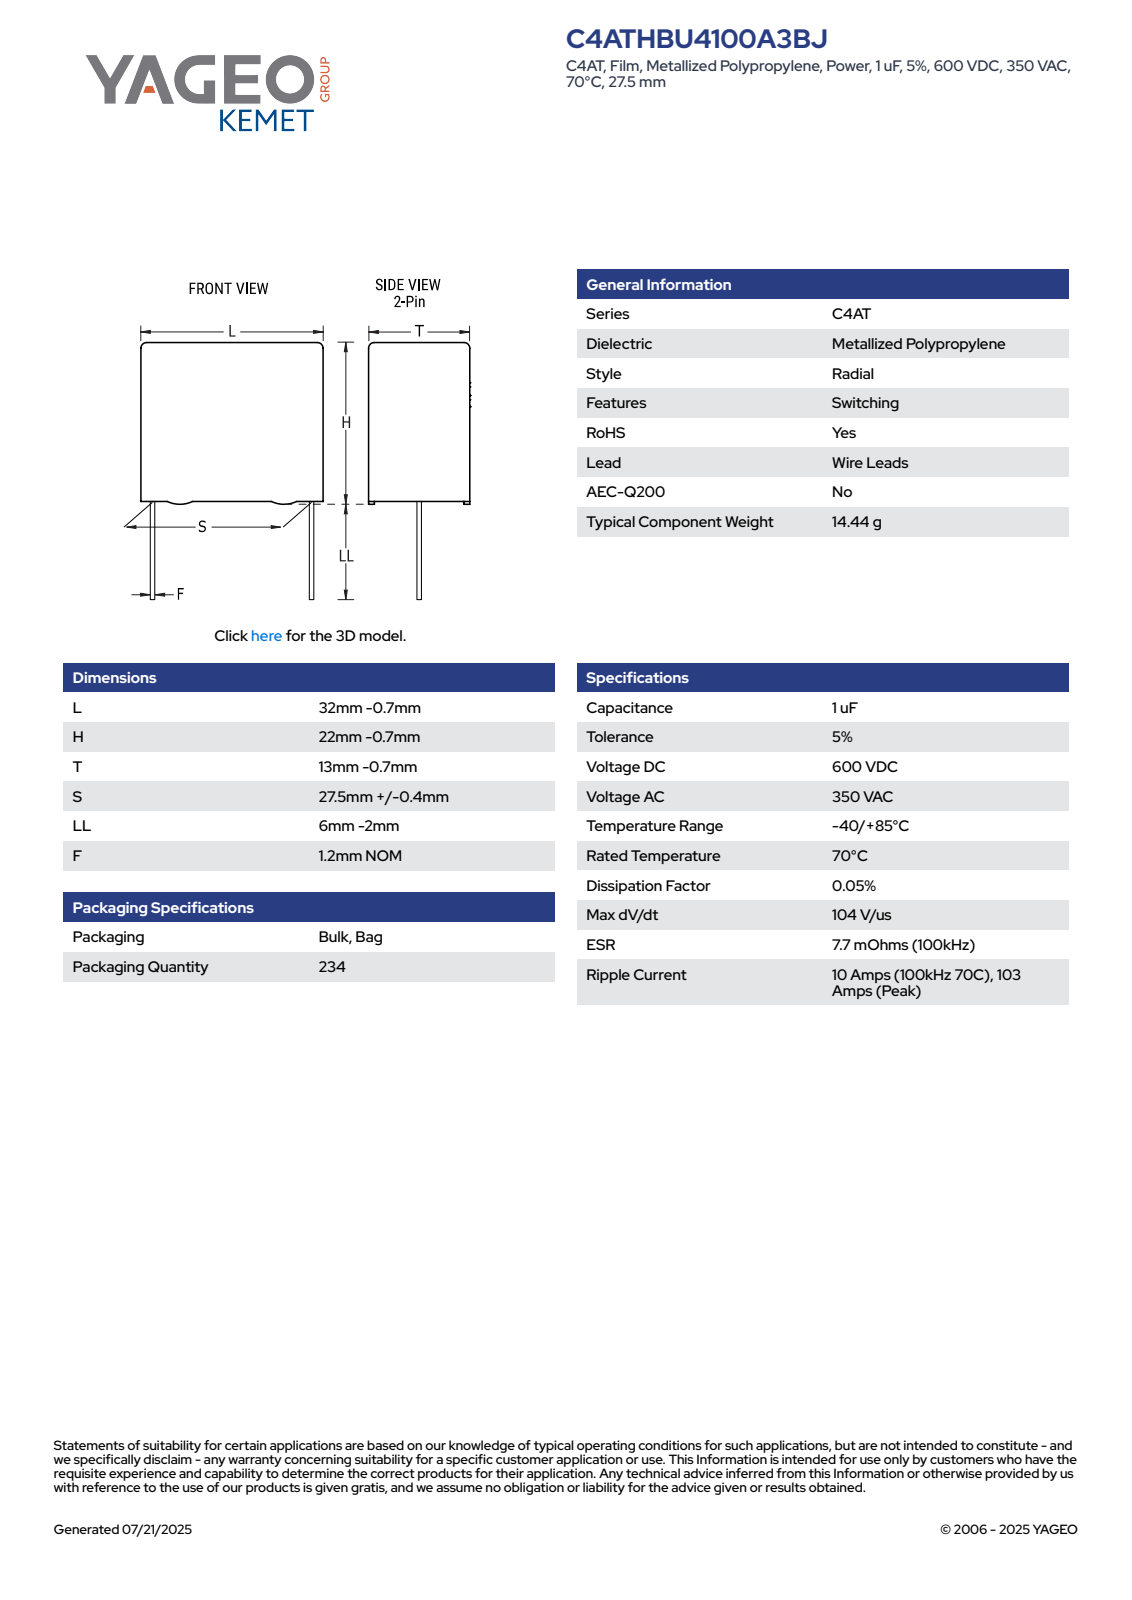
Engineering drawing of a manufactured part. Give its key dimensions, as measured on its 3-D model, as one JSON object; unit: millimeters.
{"part_name": "CFP_RB_32X22X13_L31.3H21.3T12.3S27.5LL4F1.2", "step_written_by": "SolidWorks 2014 (AUTOMOTIVE_DESIGN)", "units": "millimeters", "bodies": {"solids": 4, "faces": 89, "planar": 81, "cylindrical": 8, "other": 0}, "overall_size": [31.3, 25.3, 12.3], "volume_mm3": 8047, "surface_area_mm2": 2667, "round_bosses_or_shafts": [[1.2, 2]], "partial_cylinders_radius": [[0.5, 4]], "face_to_face_distances": [12.3, 20.87, 31.3, 0.43, 21.3, 0.7, 11.6, 10.9, 4, 4.43]}
